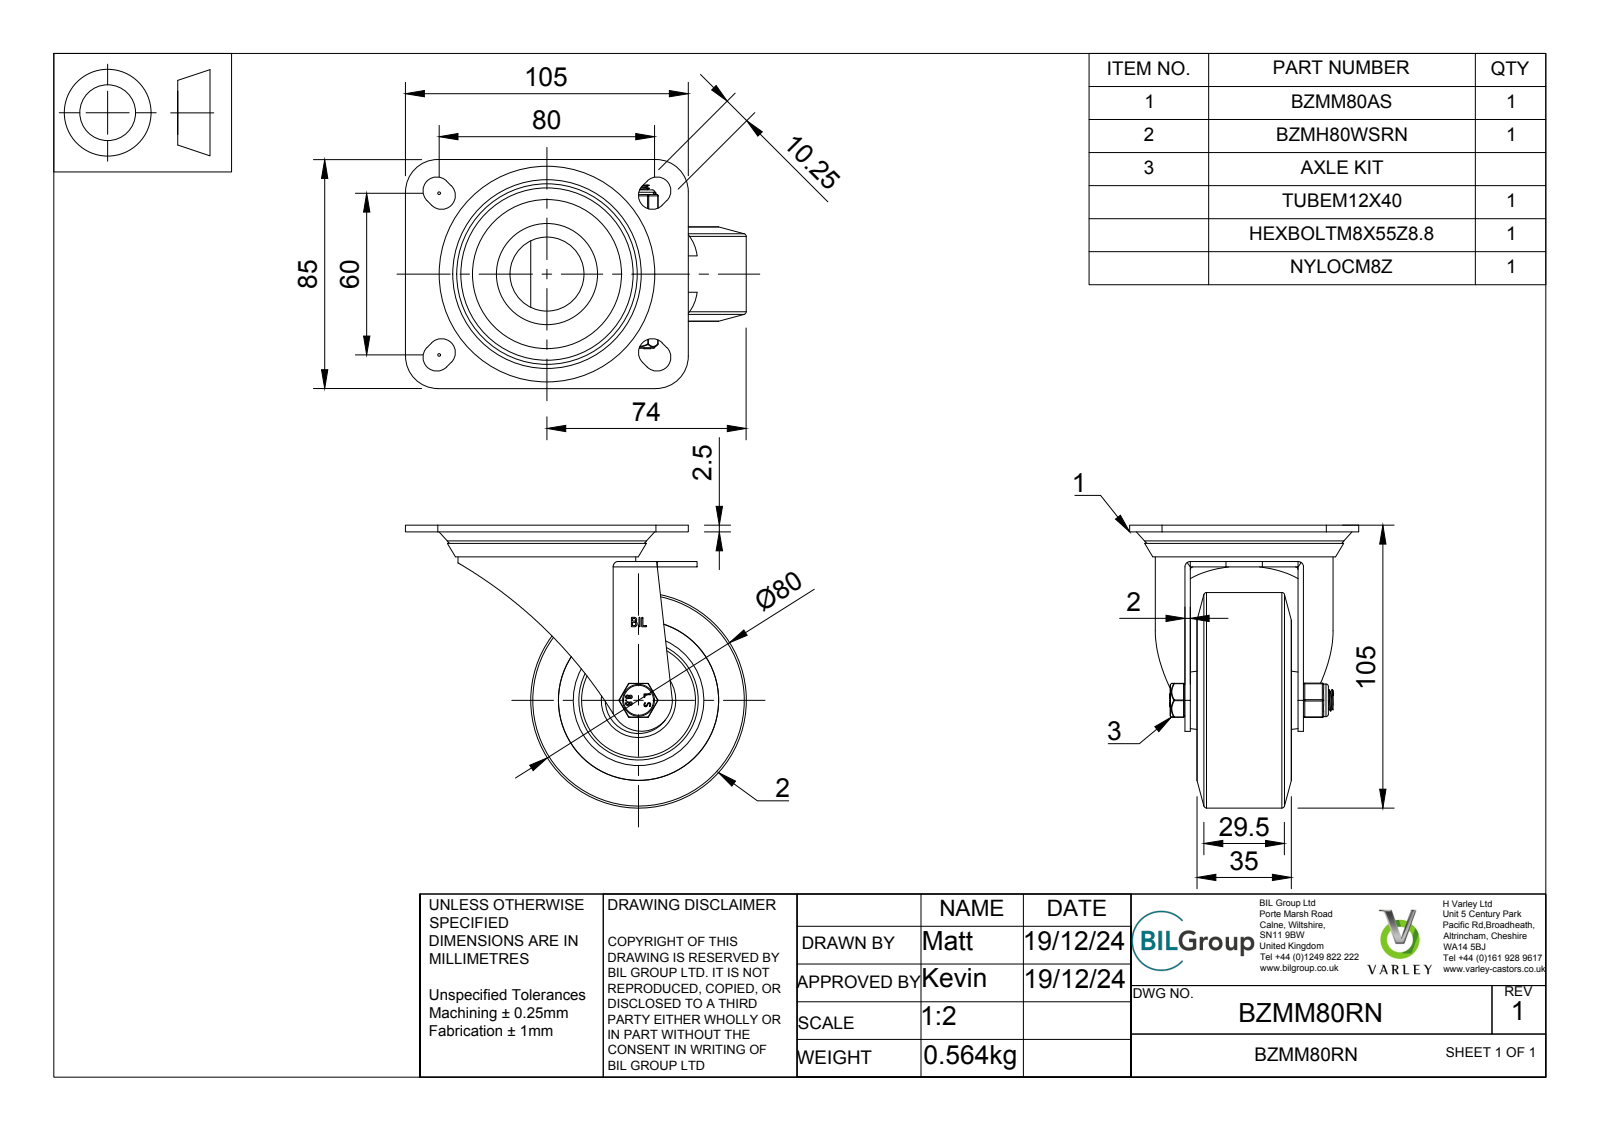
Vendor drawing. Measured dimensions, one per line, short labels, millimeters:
name: BZMM80RN v3; BZMM80AS - 2 v1; ZINC PLATED, PRESSED STEEL TOP PLATE 1; ZINC PLATED, PRESSED STEEL TOP PLATE 1 Geometry (+7 more)
written by: Autodesk Translation Framework v13.20.0.188 (AP242_MANAGED_MODEL_BASED_3D_ENGINEERING_MIM_LF)
unit: mm
bodies: 33 solids, 380 faces (119 planar, 138 cylindrical, 123 other)
size: 126.5 × 105 × 85
volume: 188 534 mm³; area: 89 705 mm²
holes: 2× ⌀0.66, 1× ⌀8, 1× ⌀8.2, 1× ⌀8.4, 1× ⌀8.6, 1× ⌀12.2, 1× ⌀27.5, 1× ⌀48, 1× ⌀59.5, 1× ⌀62
bosses: 1× ⌀80, 1× ⌀66, 1× ⌀31.5, 1× ⌀12.1, 1× ⌀11.9, 1× ⌀11.5, 1× ⌀7.87, 1× ⌀6.45
rounds: 18× R0.5, 12× R0.25, 8× R5.12, 4× R0.33, 4× R0.64, 4× R1, 4× R12, 2× R0.63
face distances: 2.5, 2, 13.5, 4.5, 42, 8, 10.5, 0.5, 8.5, 39.5
hole spacings: 3.22, 2.49
